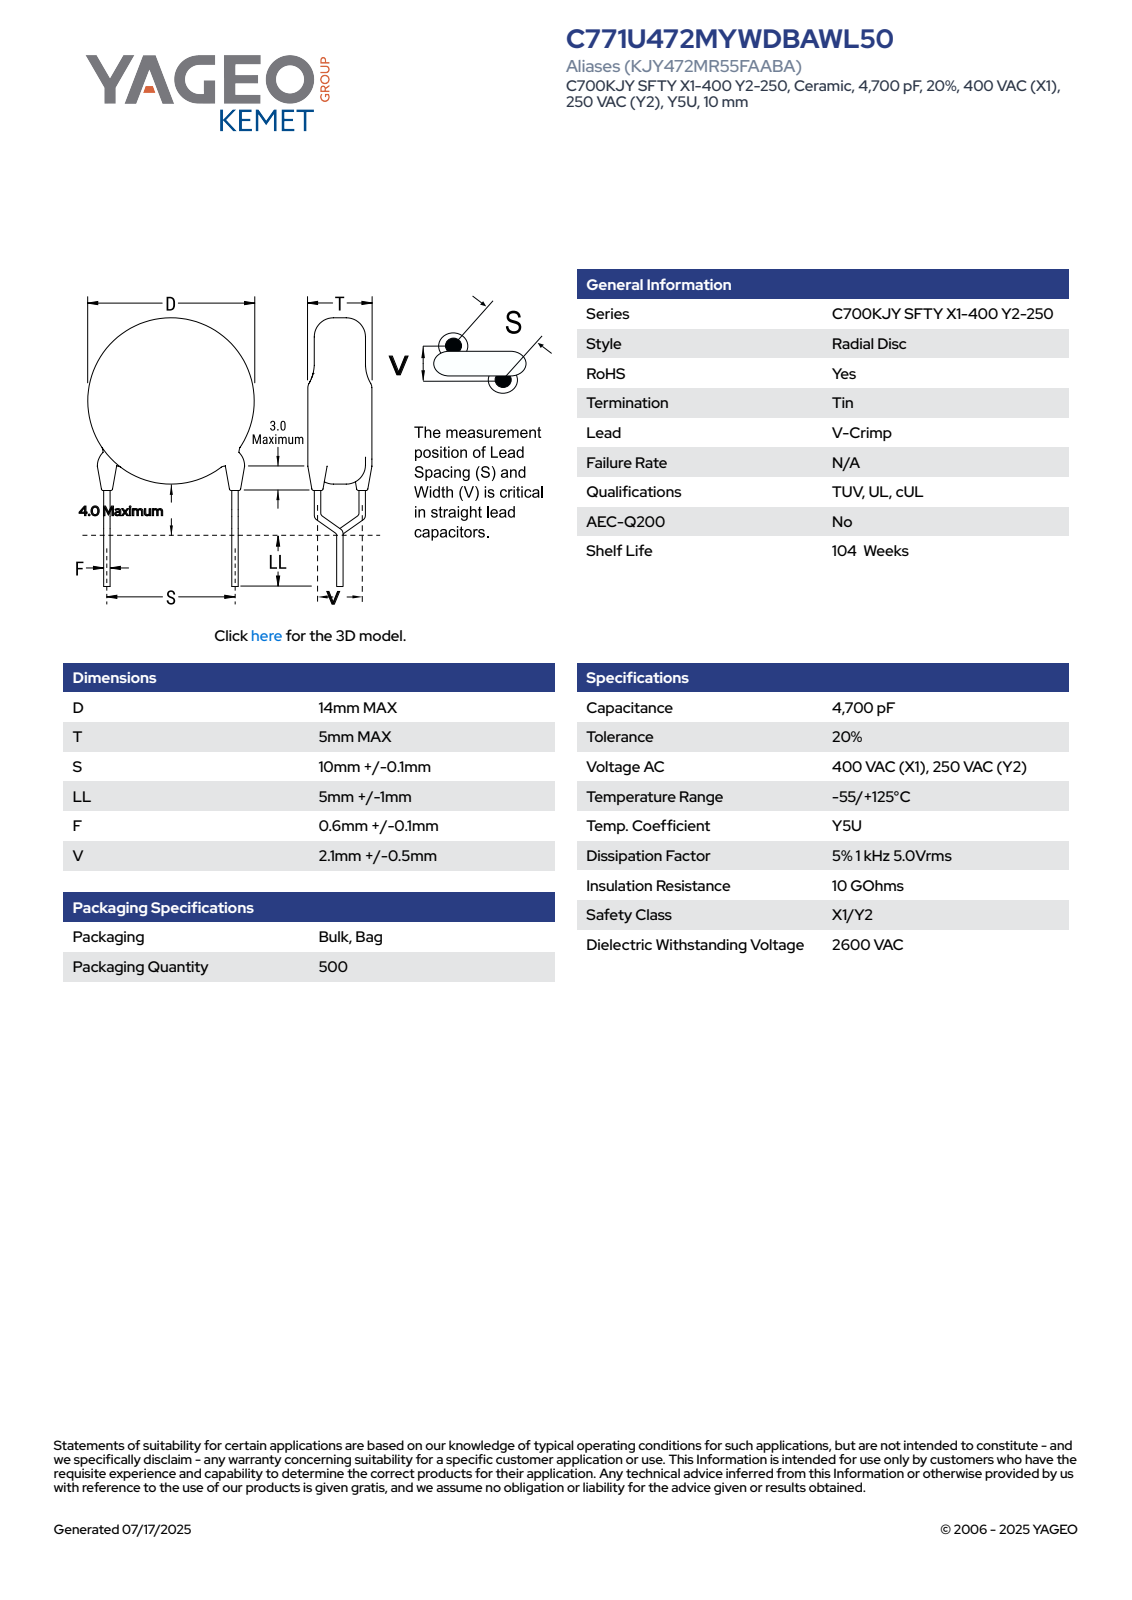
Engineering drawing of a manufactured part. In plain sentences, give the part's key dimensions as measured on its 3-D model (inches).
The part is named "CCD_VC14X5_D14T5S10LL6F0.7V2.1". Its 3-D file was written by "SolidWorks 2021 (AUTOMOTIVE_DESIGN)". It is 4 solids with 85 faces: 63 planar, 18 cylindrical and 4 other. Overall it measures 0.787 by 0.551 by 0.197 inches. Its volume is 0.046 cubic inches and its surface area 0.86 square inches. Round bosses or shafts: 6 of diameter 0.028, 2 of diameter 0.047, 1 of diameter 0.551. The main face-to-face distances are 0.197, 0.236, 0.565, 0.329, 0.489, 0.252, 0.076, 0.021, 0.312, 0.015.
